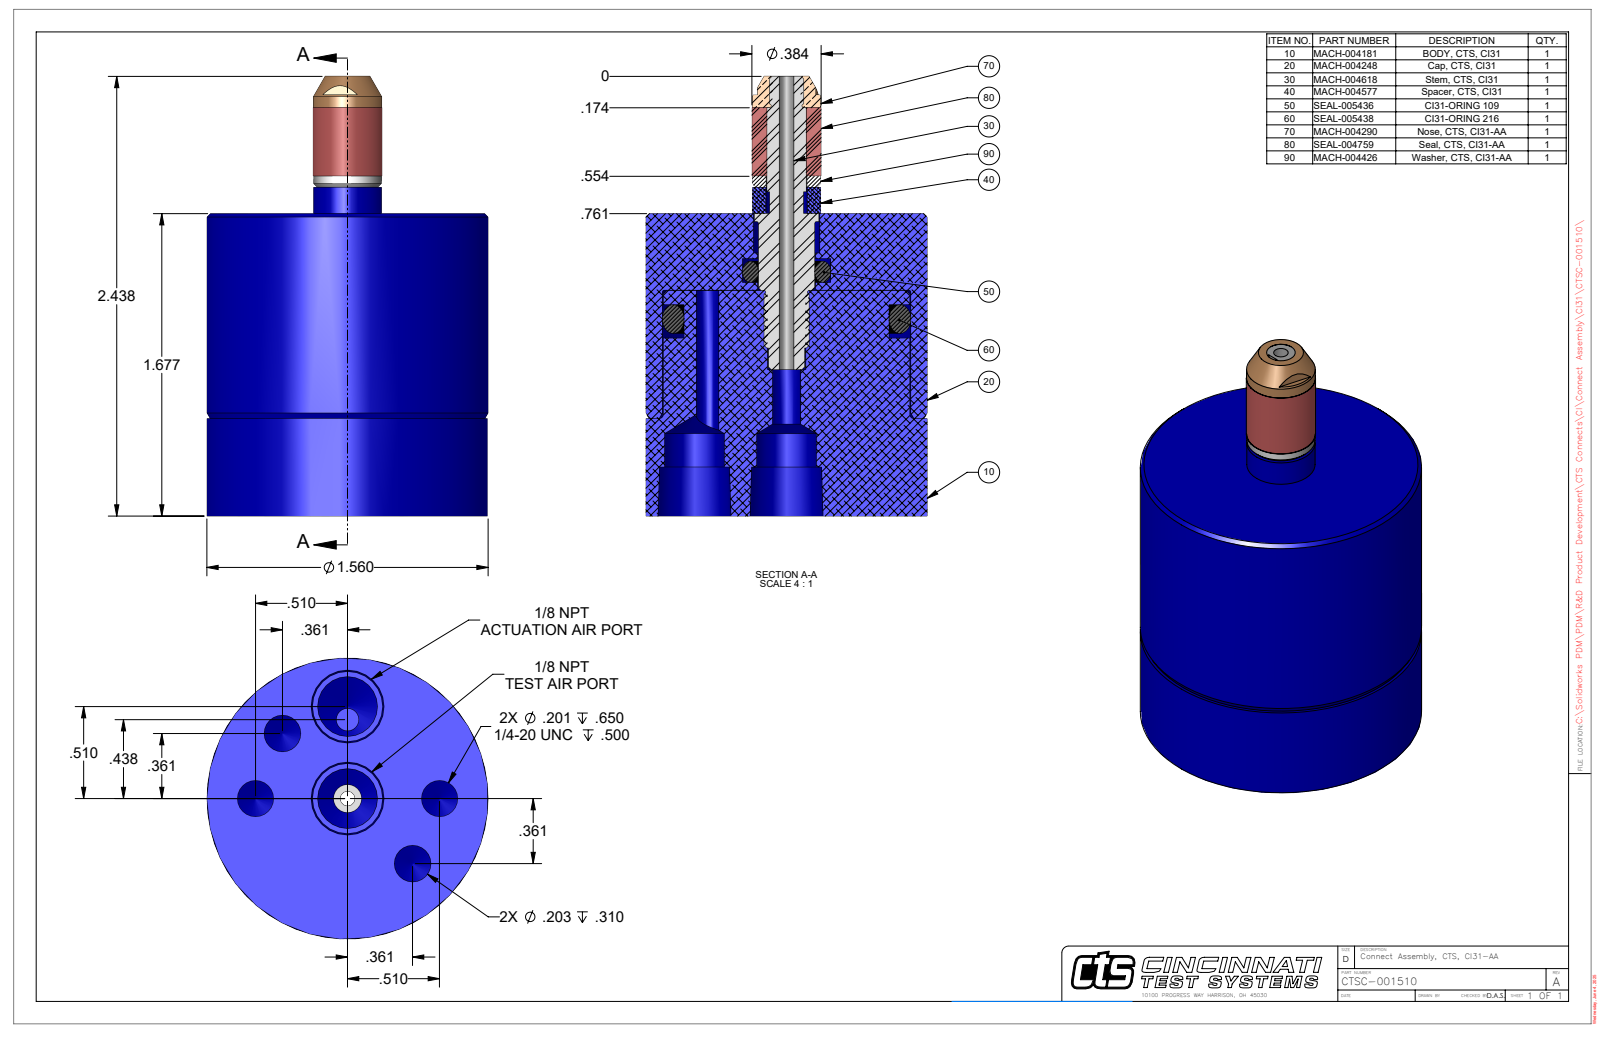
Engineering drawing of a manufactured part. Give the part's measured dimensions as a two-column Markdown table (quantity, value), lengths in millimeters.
| quantity | value |
| --- | --- |
| part name | CTSC-001510 |
| STEP written by | SolidWorks 2023 (AUTOMOTIVE_DESIGN) |
| units | millimeters |
| bodies | 1 solid, 85 faces (19 planar, 38 cylindrical, 28 other) |
| overall size | 61.9 × 39.6 × 39.6 |
| volume | 50 670 mm³ |
| surface area | 11 900 mm² |
| round holes (diameter × count) | 5.1 × 2, 5.2 × 2, 8.4 × 2, 2.1 × 1, 3.2 × 1, 4 × 1, 9.3 × 1, 35 × 1 |
| round bosses / shafts (diameter × count) | 39.6 × 1, 34.7 × 1, 9.8 × 1, 9.7 × 1, 9.6 × 1, 9.1 × 1 |
| main face-to-face distances | 42.6, 13.8, 28.8, 20.6, 6.9, 22, 61.9, 48.2, 41.3, 19.3 |
| hole center spacings | 13, 9.9, 23.9, 17.1, 18.3, 1.8, 9.4, 11.1 |
